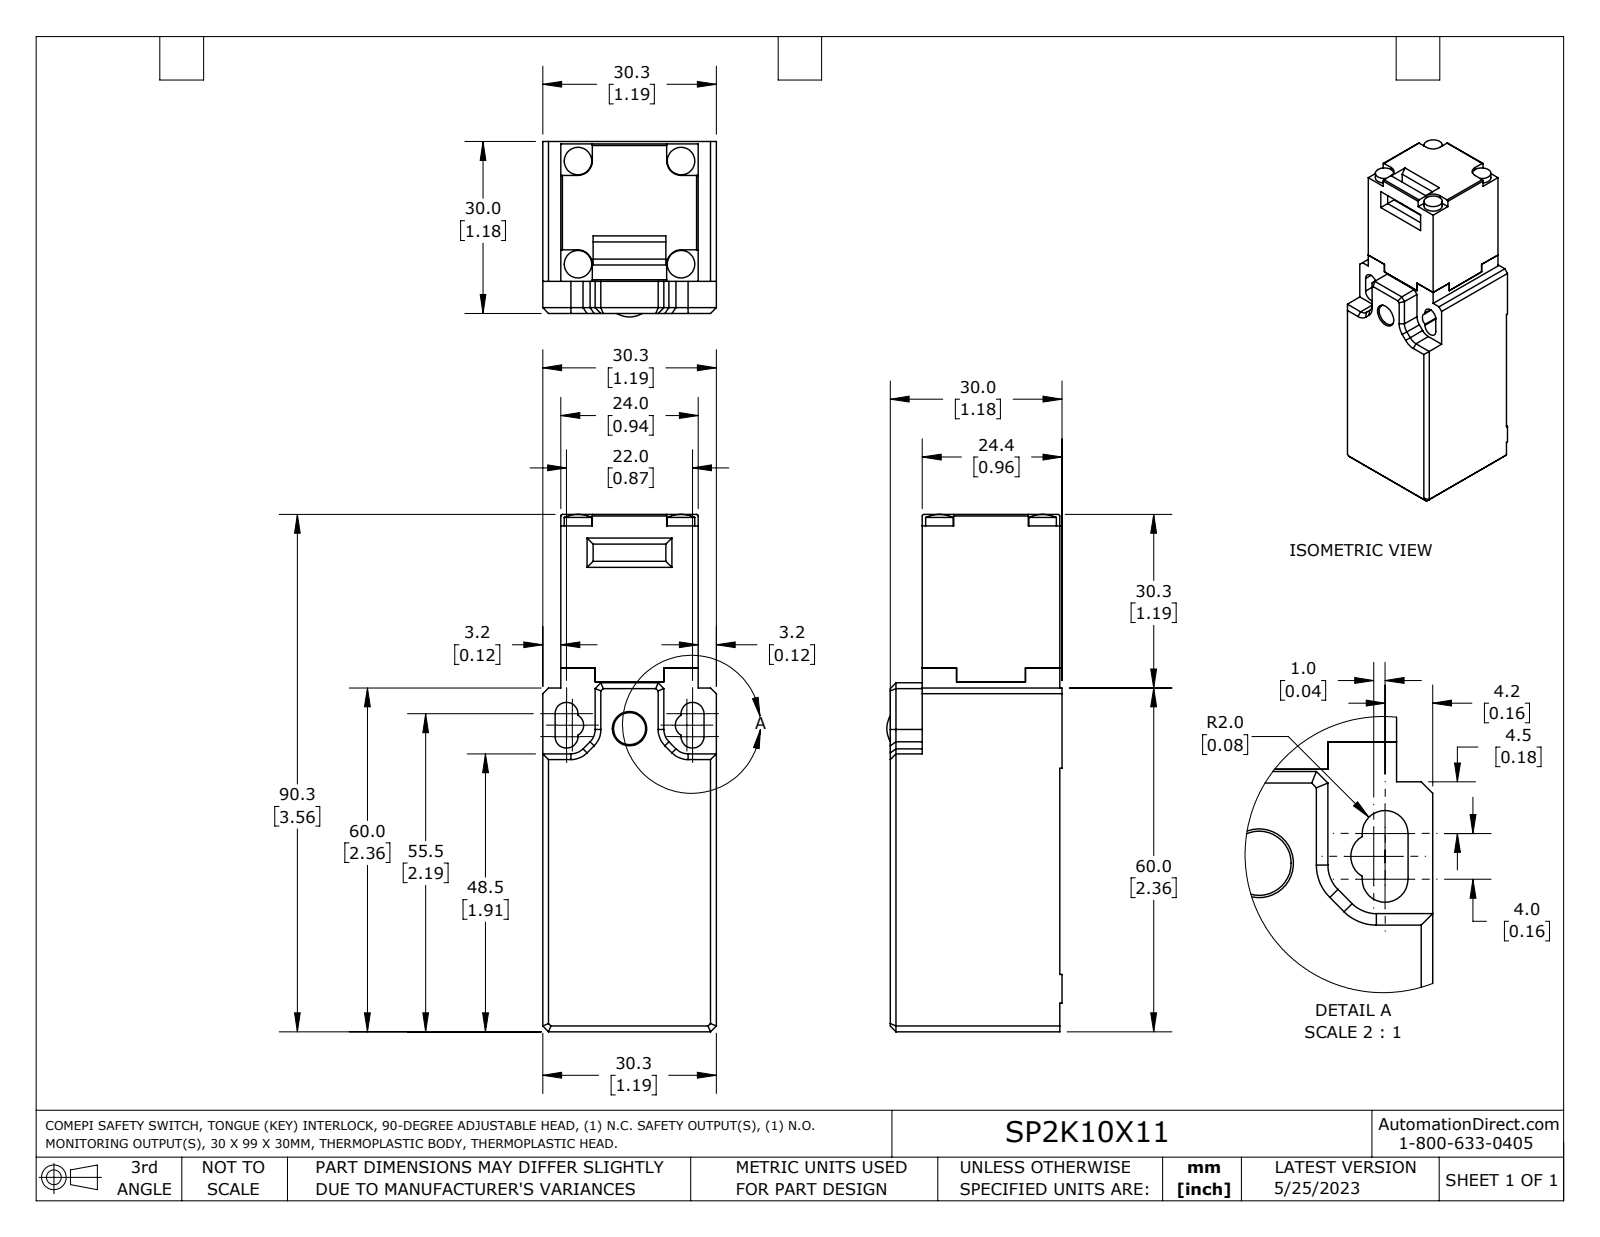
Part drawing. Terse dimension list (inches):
name: SP2K10X11
written by: SolidWorks 2021 (AUTOMOTIVE_DESIGN)
unit: in
bodies: 2 solids, 156 faces (112 planar, 34 cylindrical, 10 other)
size: 3.555 × 1.205 × 1.193
volume: 4.001 in³; area: 24.3 in²
holes: 1× ⌀0.236, 1× ⌀0.669, 1× ⌀0.748
bosses: 4× ⌀0.189, 1× ⌀0.22
rounds: 6× R0.079, 4× R0.012, 4× R0.098, 4× R0.118, 1× R0.394, 1× R0.4
face distances: 1.193, 0.945, 1.165, 0.124, 1.069, 0.22, 2.406, 0.016, 0.961, 1.181
